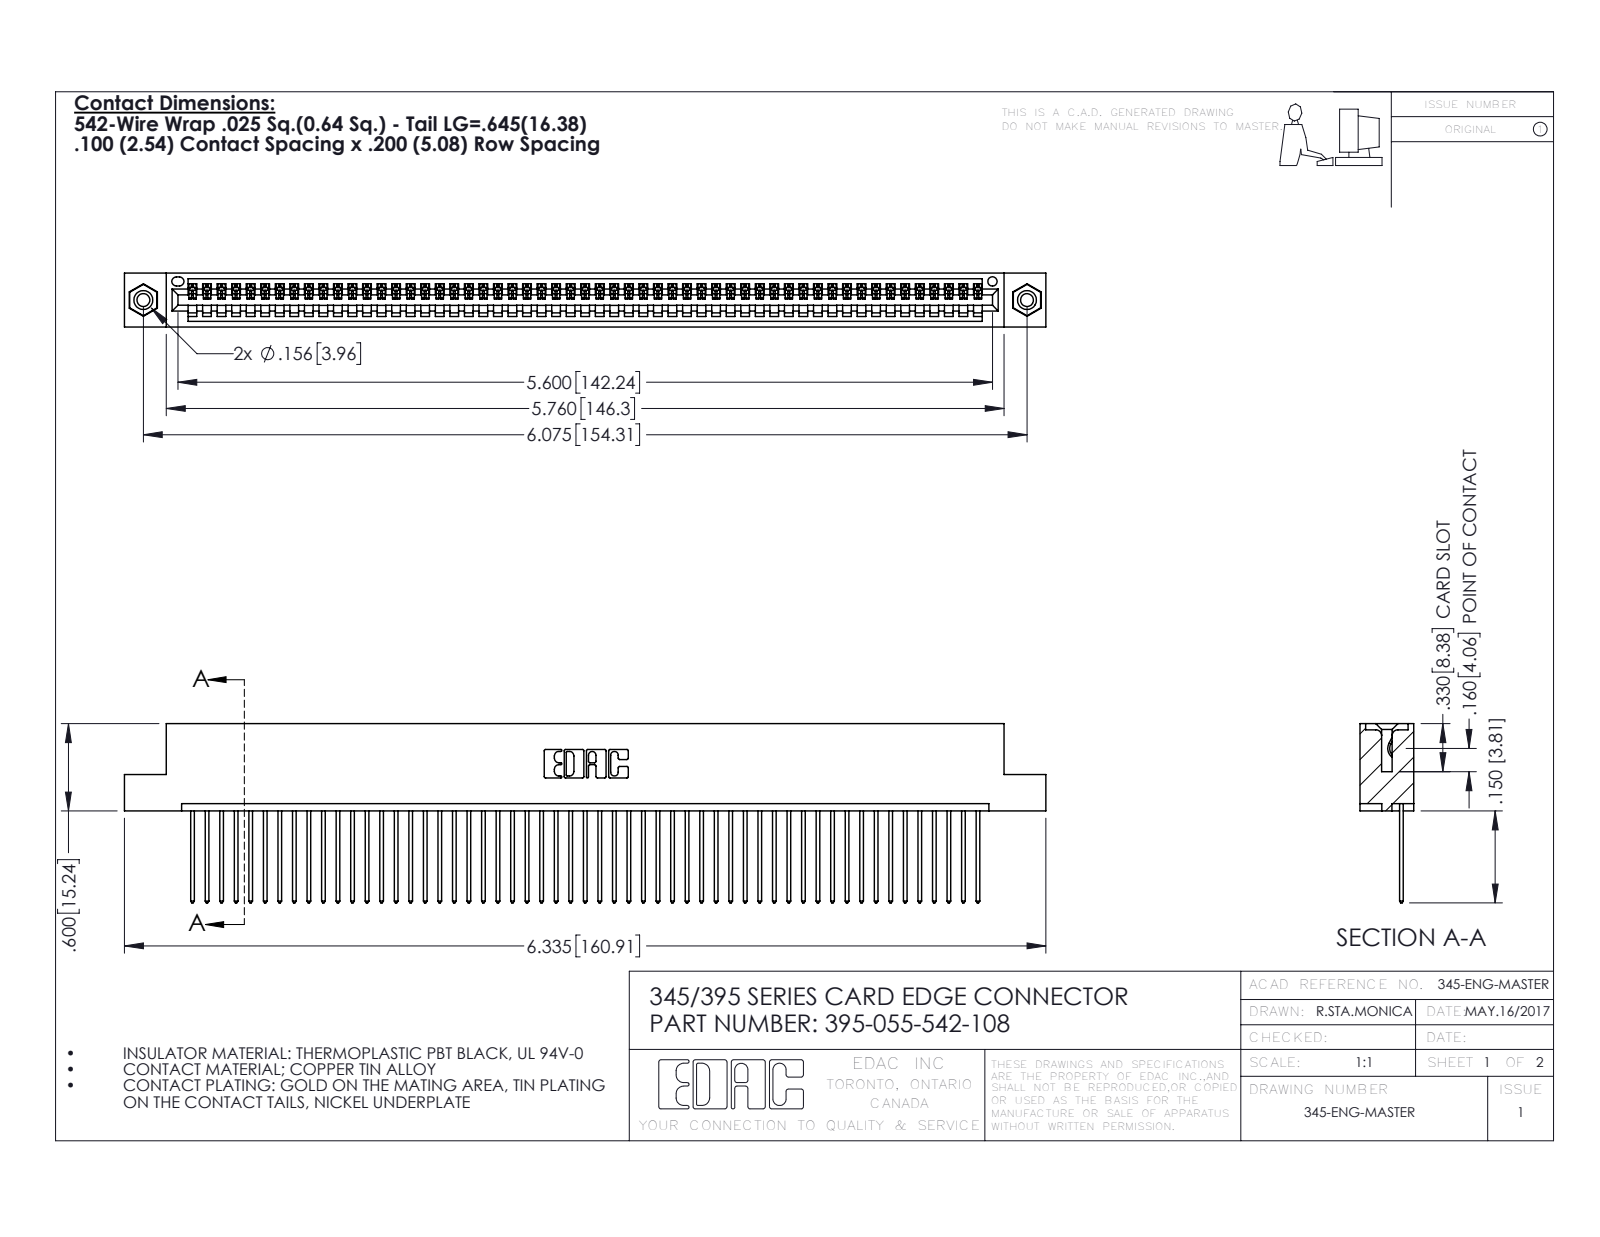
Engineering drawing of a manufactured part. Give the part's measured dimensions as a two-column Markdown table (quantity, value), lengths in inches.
| quantity | value |
| --- | --- |
| part name | 345 Part_Flush Mounting Lugs - 0.156 Dia-TI; 345-292-001_345-293-142; 395-055-542-108; 345-250-001_345-250-003-102 |
| STEP written by | SolidWorks 2016 (CONFIG_CONTROL_DESIGN) |
| units | inches |
| bodies | 58 solids, 3376 faces (2312 planar, 1048 cylindrical, 16 other) |
| overall size | 6.335 × 1.232 × 0.37 |
| volume | 0.946 in³ |
| surface area | 33.44 in² |
| round holes (diameter × count) | 0.089 × 2, 0.125 × 2, 0.156 × 2, 0.064 × 1 |
| round bosses / shafts (diameter × count) | 0.155 × 2 |
| partial cylindrical surfaces (radius × count) | 0.006 × 110, 0.01 × 110, 0.01 × 22, 0.007 × 6, 0.031 × 6, 0.026 × 3, 0.031 × 2, 0.04 × 2 |
| main face-to-face distances | 0.072, 0.298, 0.098, 0.272, 0.025, 0.37, 0.2, 0.225, 0.149, 0.072 |
| hole center spacings | 0.27, 5.839, 6.075 |
